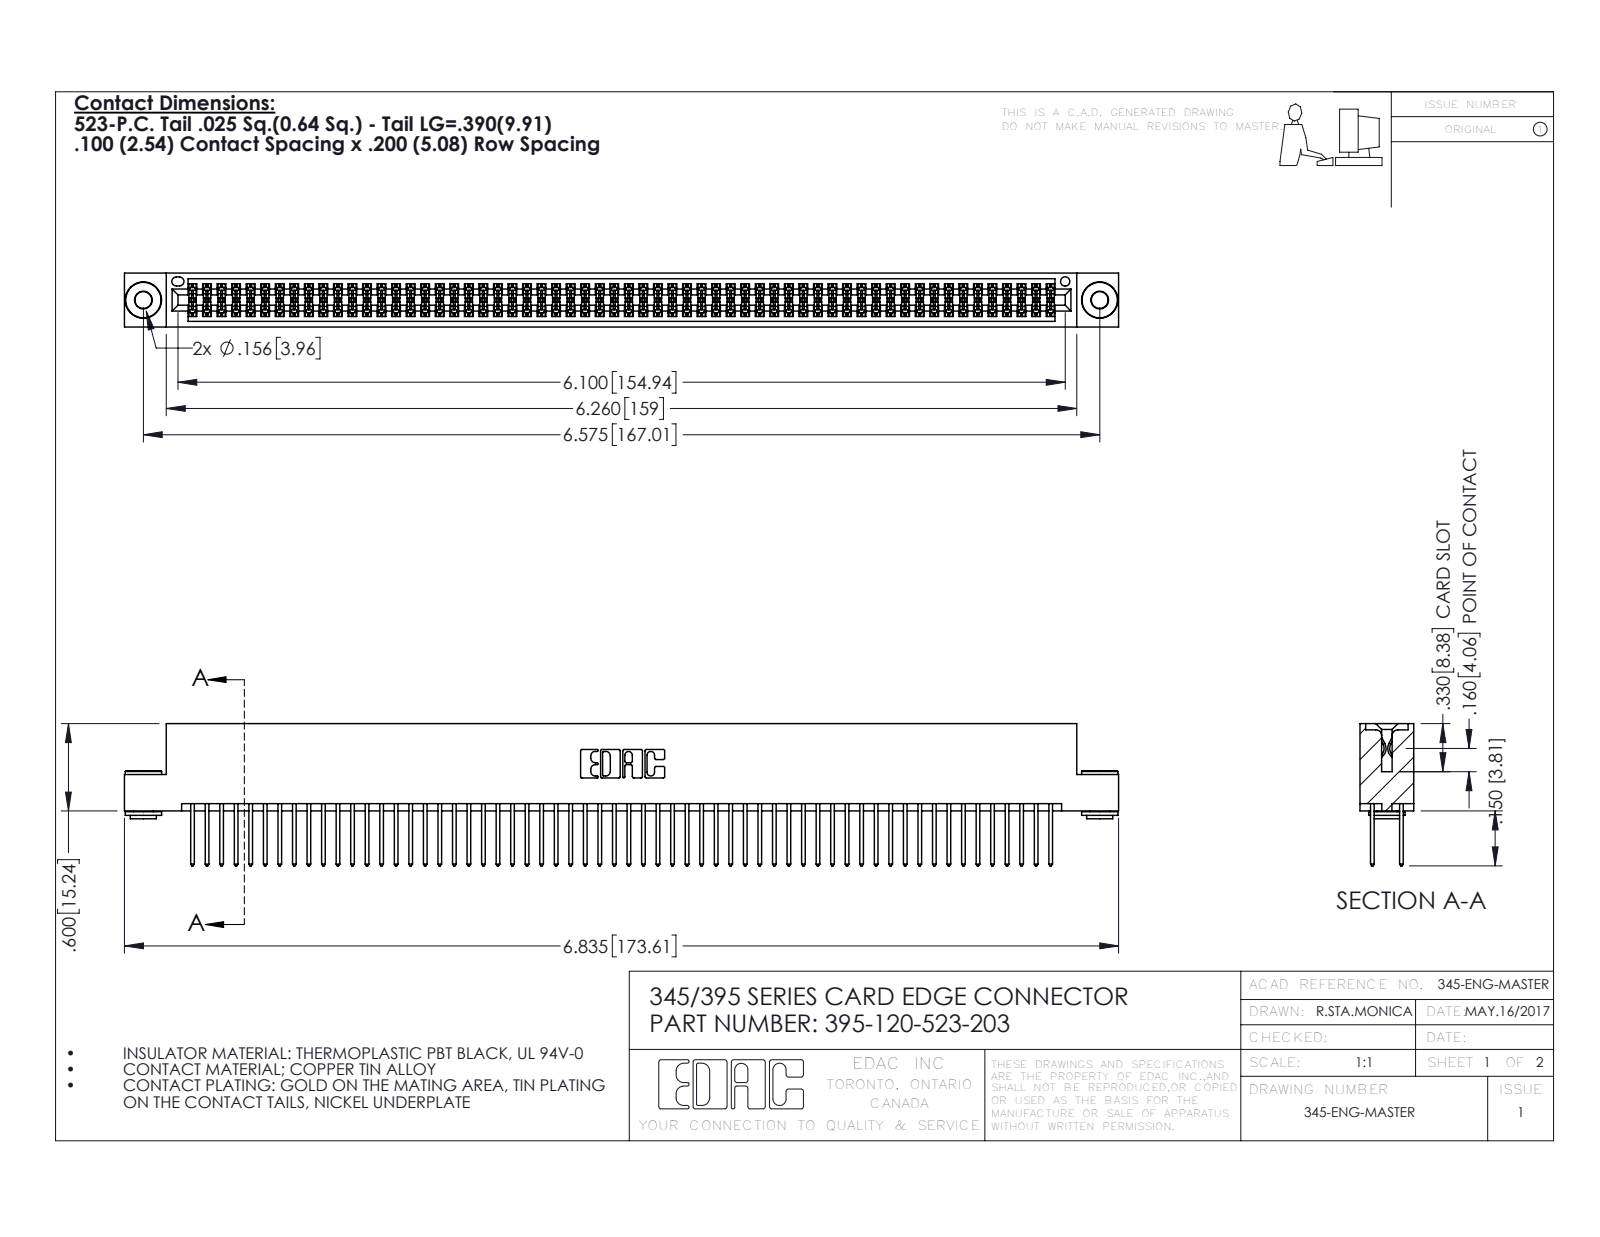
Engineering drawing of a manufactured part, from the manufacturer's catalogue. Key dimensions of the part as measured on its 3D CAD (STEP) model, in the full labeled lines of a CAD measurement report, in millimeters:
Part name (STEP PRODUCT): 345-250-002_345-250-002-102; 345 Part_Flush Mounting Lugs - 0.156 Dia-TH; 395-120-523-203; 345-292-001_345-293-123
STEP written by: SolidWorks 2016 (CONFIG_CONTROL_DESIGN)
Units: millimetres
Bodies: 123 solids, 6164 faces (4050 planar, 2106 cylindrical, 8 other)
Overall size (bounding box): 173.6 × 24.8 × 9.4
Volume: 17 300 mm³ · Surface area: 27 230 mm²
Round holes (diameter × count): ⌀2.9 ×2, ⌀4 ×2, ⌀1.6 ×1
Round bosses / shafts (diameter × count): ⌀6.4 ×2, ⌀4.6 ×2, ⌀3.5 ×2
Partial cylindrical surfaces — rounded edges, fillets, slot ends (radius × count): R0.2 ×180, R0.3 ×120, R0.3 ×22, R0.2 ×6, R0.8 ×6, R0.7 ×3, R0.4 ×2, R0.5 ×2
Main face-to-face distances: 1.8, 7.6, 5.1, 0.6, 2.5, 6.9, 9.4, 5.7, 4.4, 3.8
Hole centre spacings: 6.9, 161, 167
